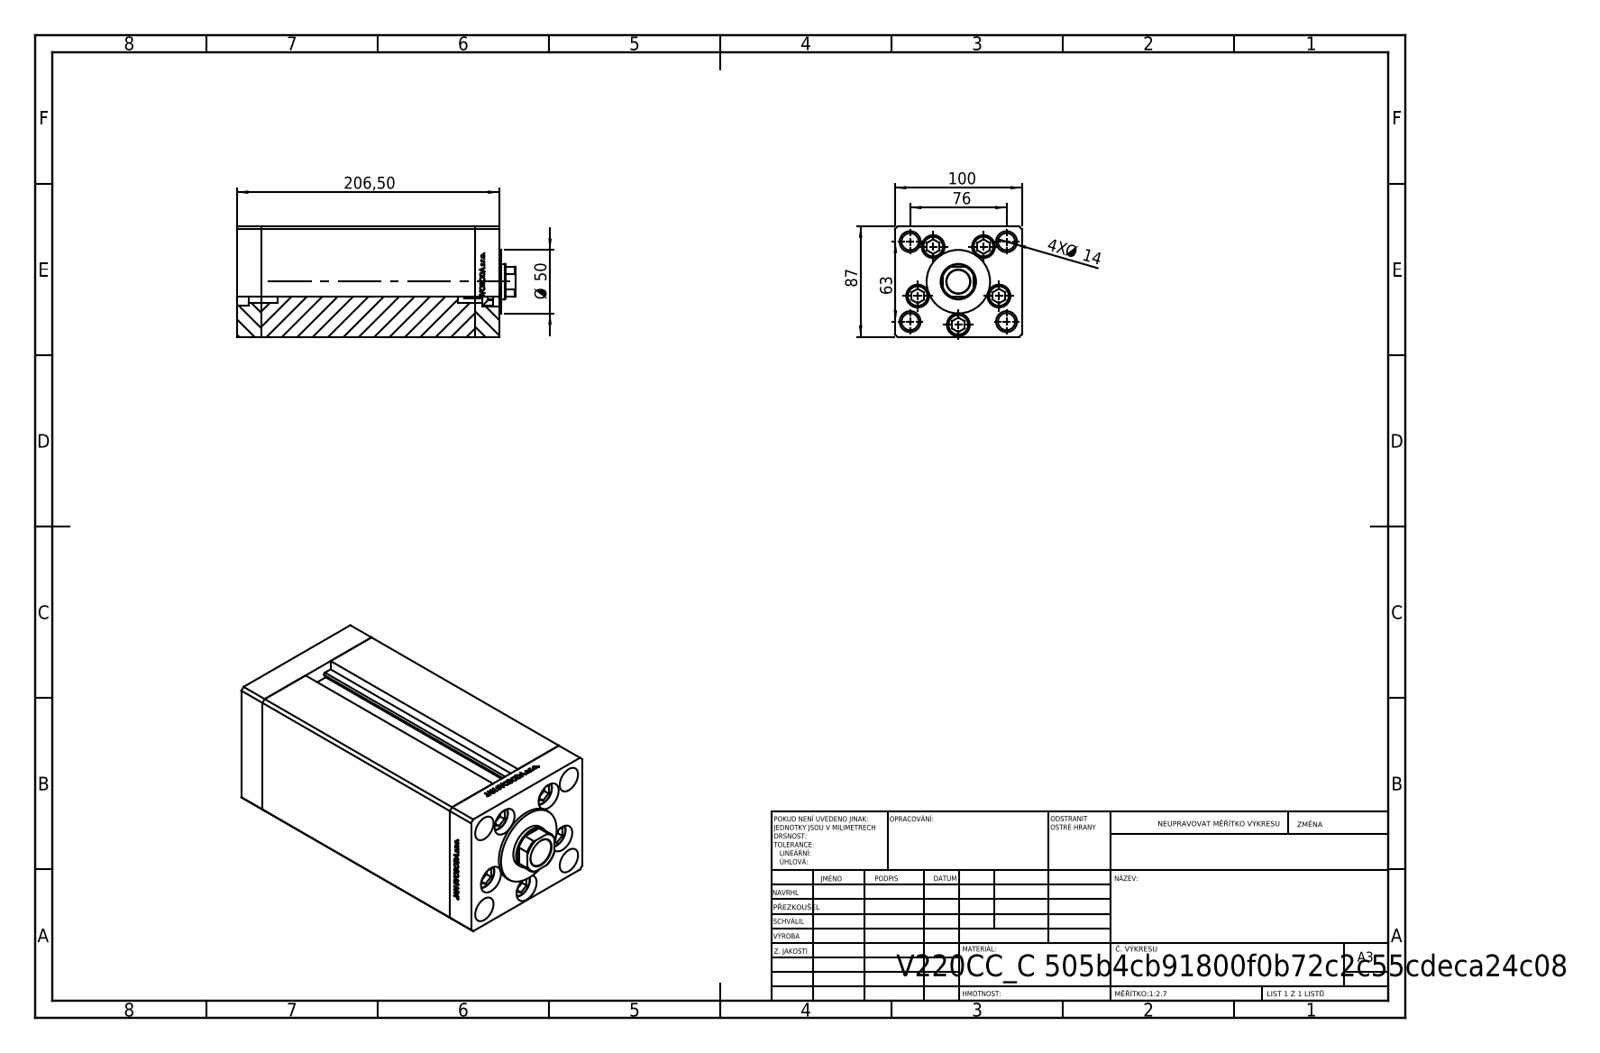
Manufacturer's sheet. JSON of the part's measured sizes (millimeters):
{"part_name": "V220C FRONT; V220C BACK_C; V220C_C MIDDLE; V220C_VC_C (+1 more)", "step_written_by": "SolidWorks 2019 (CONFIG_CONTROL_DESIGN)", "units": "millimeters", "bodies": {"solids": 13, "faces": 1164, "planar": 542, "cylindrical": 160, "other": 462}, "overall_size": [219.5, 100, 87], "volume_mm3": 1470000, "surface_area_mm2": 245103, "round_holes": [[13.5, 9], [18, 5], [12, 4], [16.5, 4], [17, 1], [18.5, 1], [28, 1]], "round_bosses_or_shafts": [[8, 5], [17, 4], [50, 1]], "partial_cylinders_radius": [[0.93, 2], [13.5, 1]], "face_to_face_distances": [100, 87, 19, 168.5, 187.5, 34.25, 206.5, 172.25, 153.25, 15.25], "hole_center_spacings": [34, 49.36, 18.59, 21.03, 38.08, 39.27, 40.83, 43.24]}
